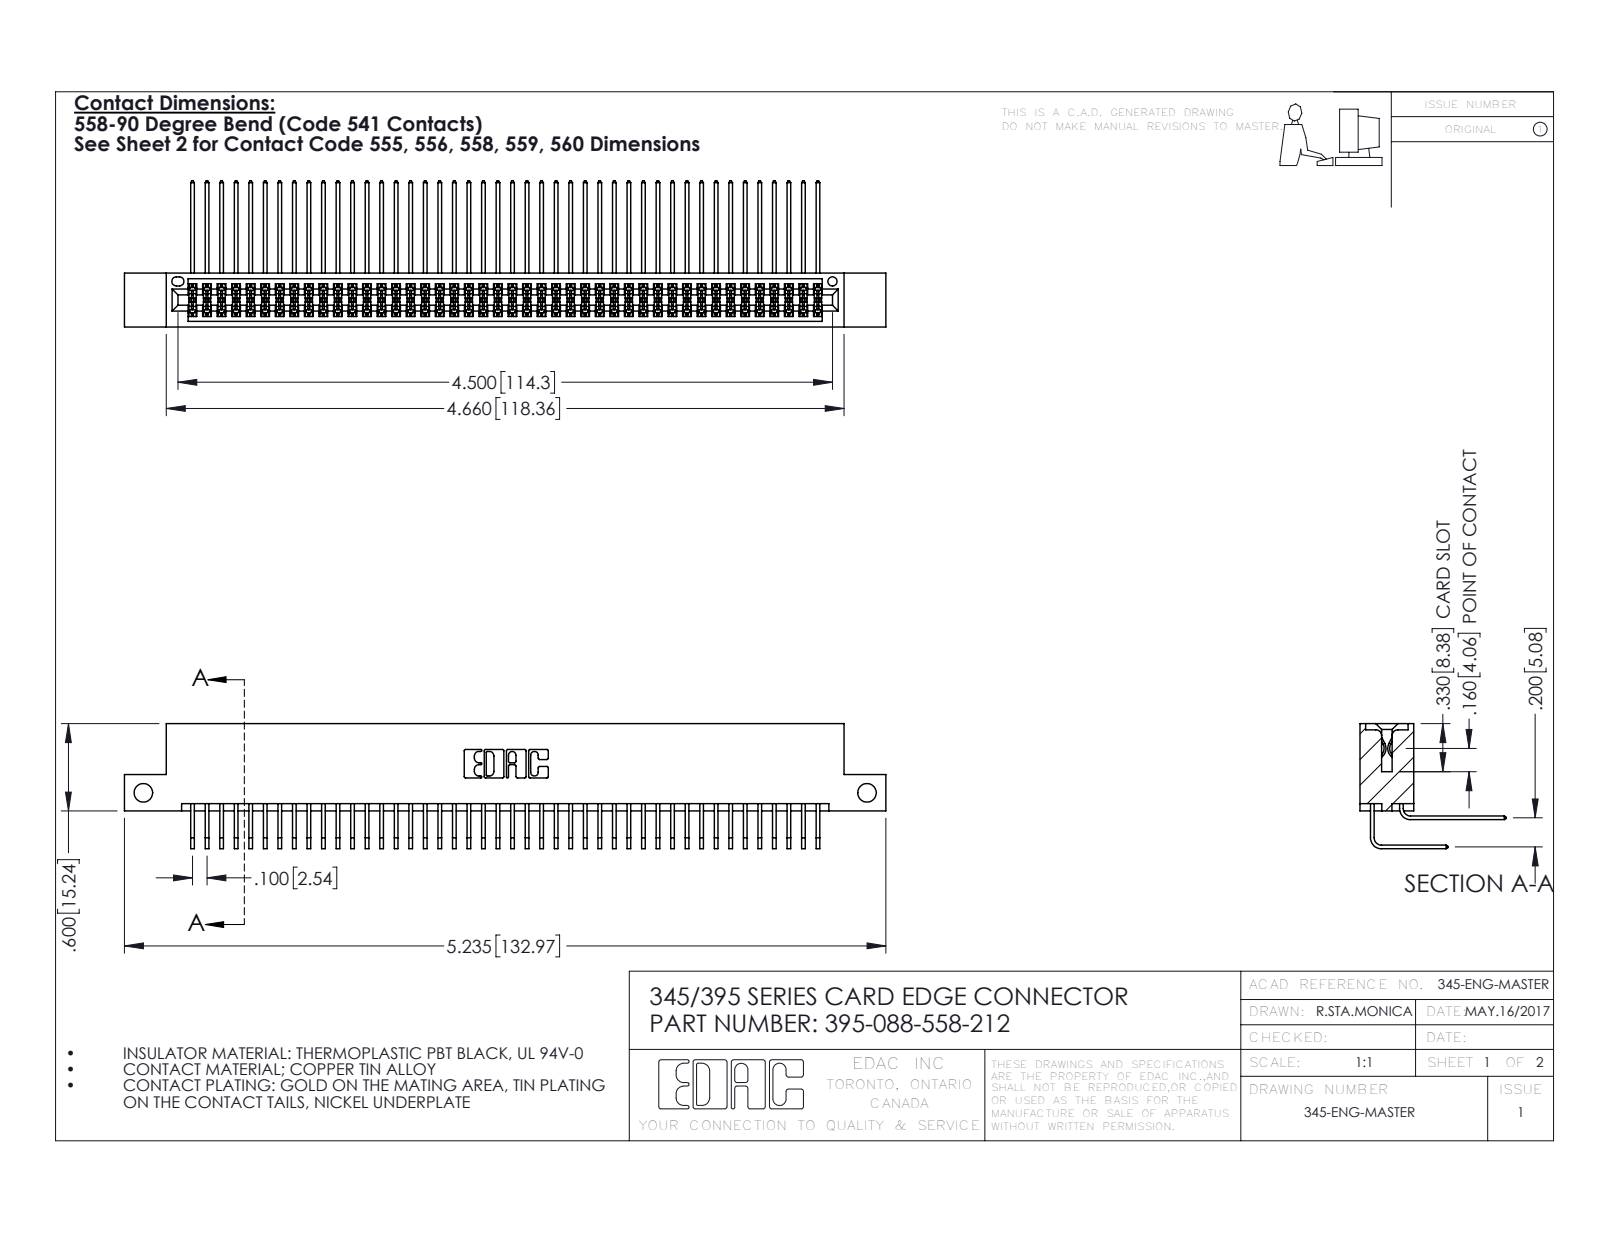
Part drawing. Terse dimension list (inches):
name: 345-292-001_558 559 Tail - 1; 395-088-558-212; 345 Part_Flush Mounting Lugs - Side Mount; 345-292-001_558 Tail - 2
written by: SolidWorks 2016 (CONFIG_CONTROL_DESIGN)
unit: in
bodies: 89 solids, 4702 faces (3160 planar, 1542 cylindrical, 0 other)
size: 5.235 × 1.005 × 0.859
volume: 0.815 in³; area: 34.15 in²
holes: 2× ⌀0.128, 1× ⌀0.064
rounds: 133× R0.006, 22× R0.01, 6× R0.007, 6× R0.031, 3× R0.026, 2× R0.014, 2× R0.019, 2× R0.022
face distances: 0.072, 0.298, 0.2, 0.37, 0.098, 0.272, 0.025, 0.225, 0.025, 0.175
hole spacings: 4.975
